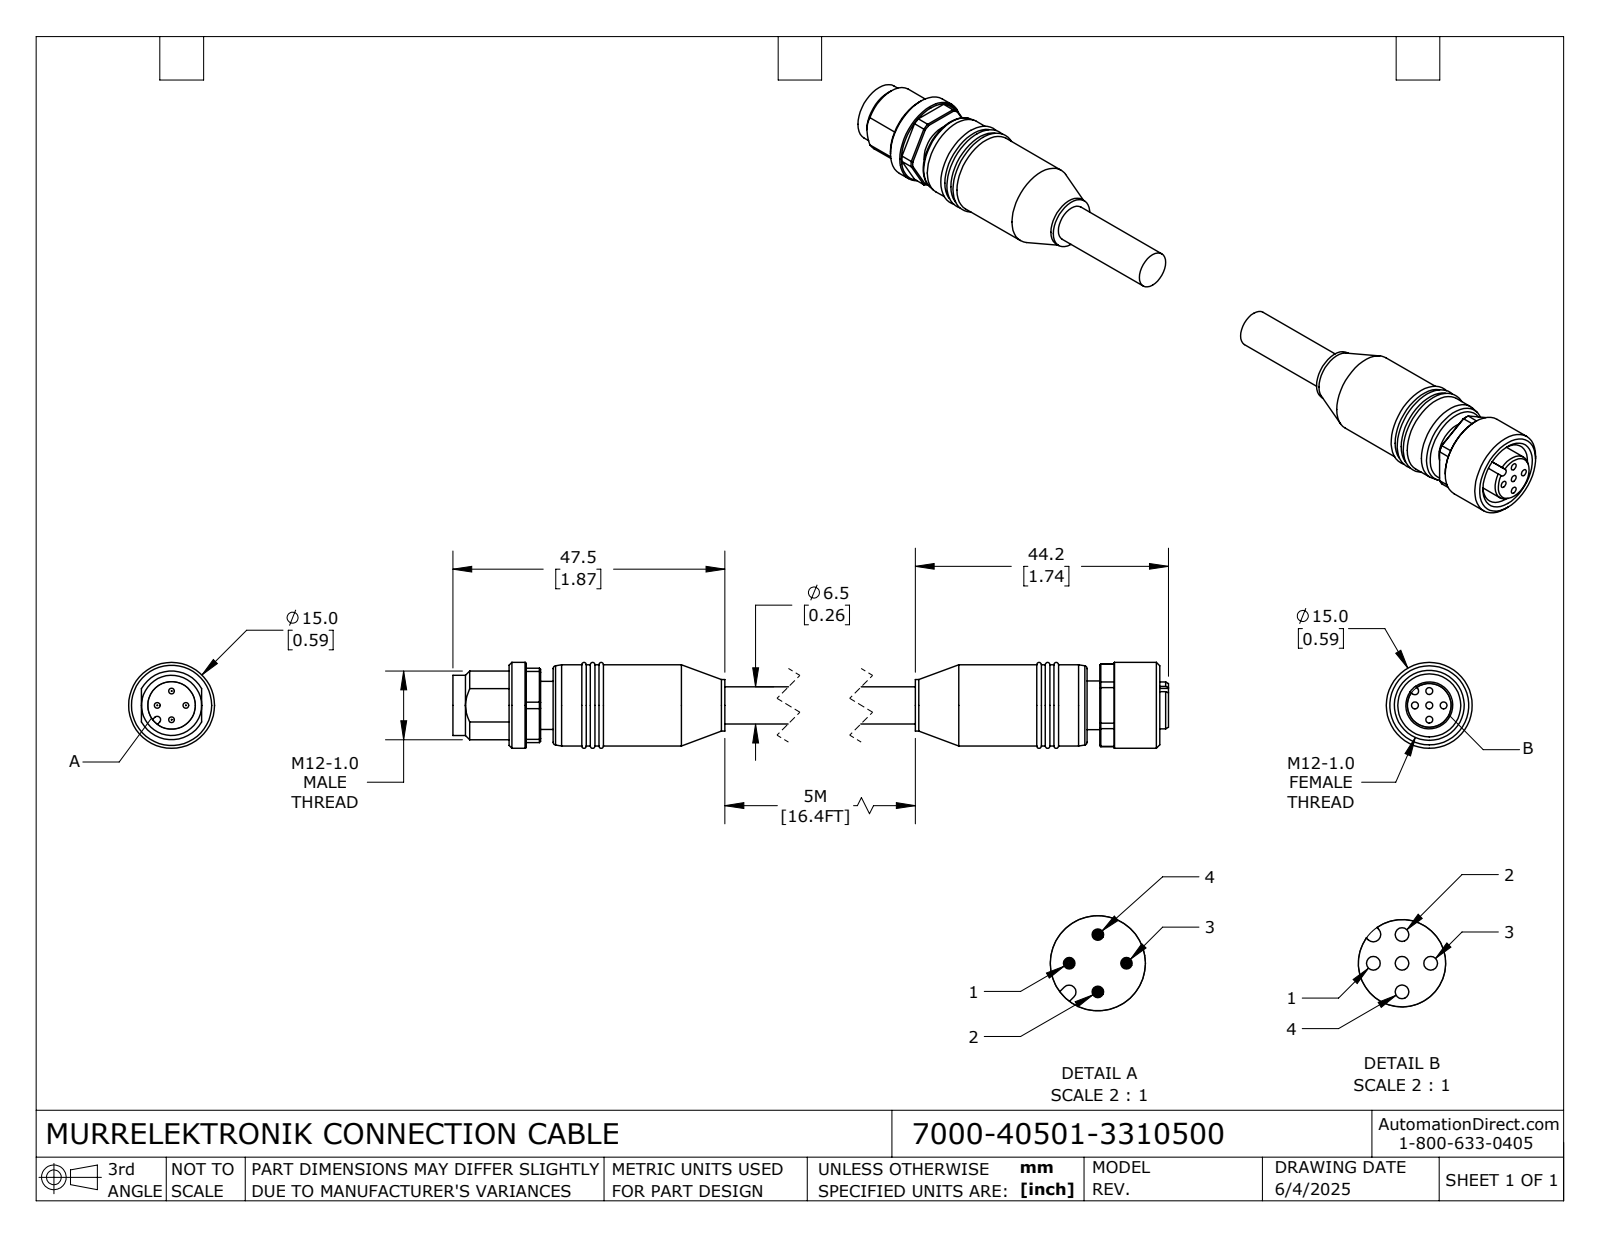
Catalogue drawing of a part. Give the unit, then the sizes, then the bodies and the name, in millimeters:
Units: millimetres
Overall size (bounding box): 156.7 × 15 × 15
Round holes (diameter × count): ⌀1.2 ×5, ⌀8.3 ×1, ⌀11 ×1
Round bosses / shafts (diameter × count): ⌀1 ×4, ⌀15 ×1, ⌀14.2 ×1, ⌀10.5 ×1, ⌀9 ×1, ⌀8.5 ×1, ⌀8.4 ×1, ⌀8.2 ×1
Partial cylindrical surfaces — rounded edges, fillets, slot ends (radius × count): R0.6 ×1, R0.65 ×1, R6 ×1, R7.2 ×1
Main face-to-face distances: 2.2, 127.2, 13, 129.4, 10.5, 125, 134.9, 52.2, 77.2, 50
Hole centre spacings: 2.5, 3.54, 5
Volume: 13 204 mm³ · Surface area: 6 518 mm²
Bodies: 2 solids, 193 faces (57 planar, 75 cylindrical, 61 other)
Part name (STEP PRODUCT): 7000-40501-3310500_FEMALE; 7000-40501-3310500; 7000-40501-3310500_MALE
STEP written by: SolidWorks 2024 (CONFIG_CONTROL_DESIGN)
